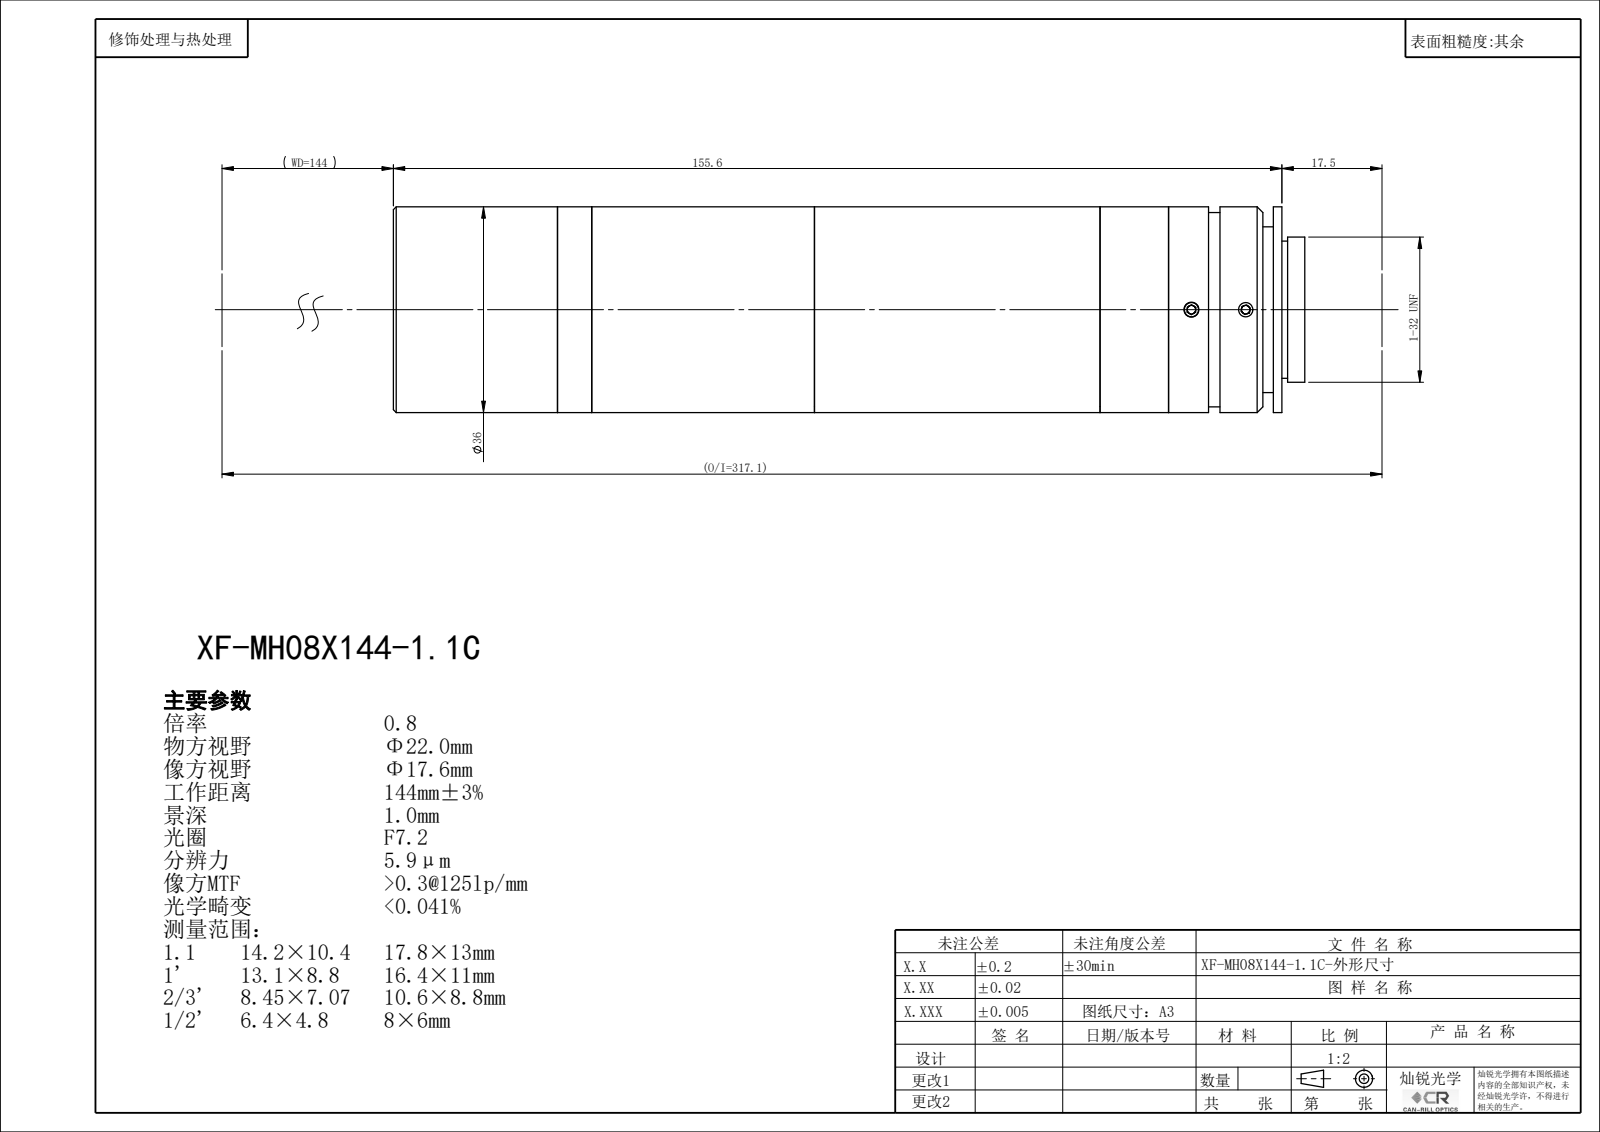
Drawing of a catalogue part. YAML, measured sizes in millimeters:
part_name: "XF-MH08X144-1.1C"
step_written_by: "SolidWorks 2022 (CONFIG_CONTROL_DESIGN)"
units: millimeters
bodies: {solids: 0, faces: 131, planar: 65, cylindrical: 44, other: 22}
overall_size: [159.56, 36, 36]
round_holes:
  - {diameter: 2.5, count: 3}
  - {diameter: 22.4, count: 1}
  - {diameter: 24, count: 1}
  - {diameter: 26, count: 1}
  - {diameter: 26.4, count: 1}
  - {diameter: 29.4, count: 1}
  - {diameter: 33.4, count: 1}
  - {diameter: 34.5, count: 1}
round_bosses_or_shafts:
  - {diameter: 36, count: 1}
  - {diameter: 34, count: 1}
  - {diameter: 29, count: 1}
  - {diameter: 25.4, count: 1}
face_to_face_distances: [19.83, 1.5, 18.33, 12, 30.33, 31.83, 50, 62, 80.33, 81.83]
